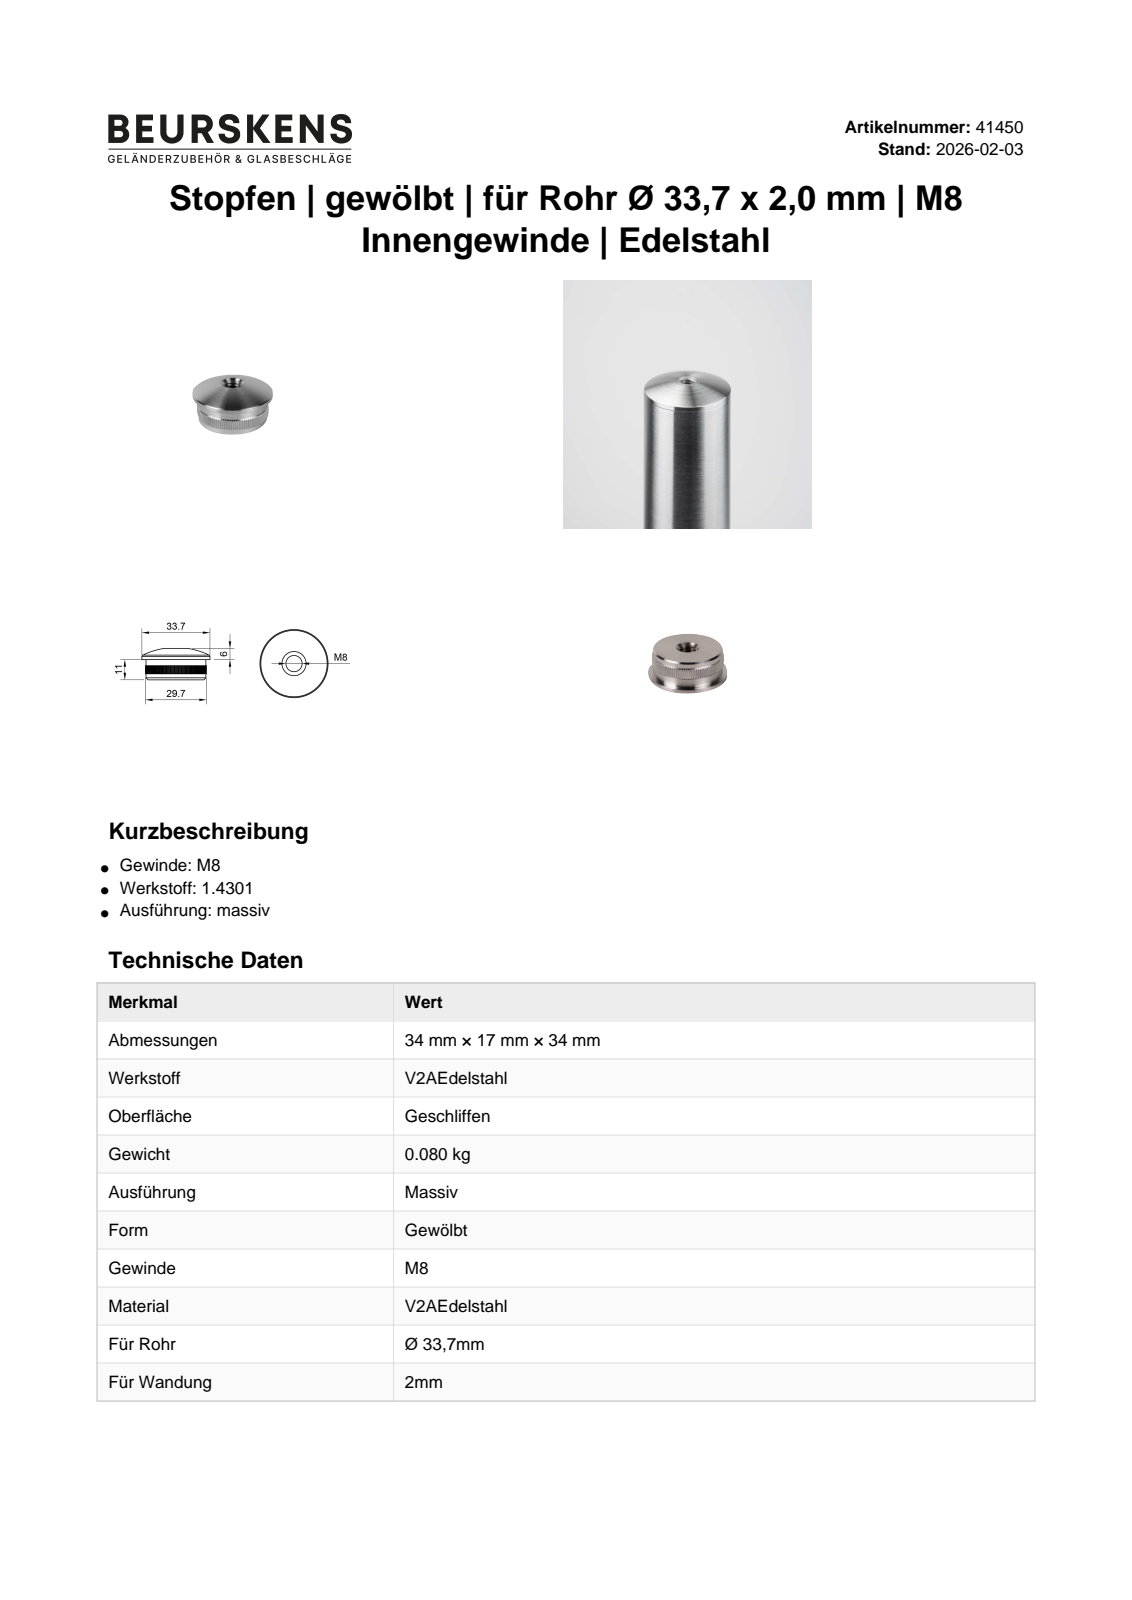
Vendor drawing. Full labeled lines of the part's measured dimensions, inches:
Part name (STEP PRODUCT): 41450
STEP written by: Autodesk Inventor 2022 (AUTOMOTIVE_DESIGN)
Units: inches
Bodies: 1 solid, 293 faces (4 planar, 284 cylindrical, 5 other)
Overall size (bounding box): 1.327 × 1.327 × 0.611
Volume: 0.586 in³ · Surface area: 5.086 in²
Round holes (diameter × count): ⌀0.315 ×1
Round bosses / shafts (diameter × count): ⌀1.327 ×1, ⌀1.165 ×1
Partial cylindrical surfaces — rounded edges, fillets, slot ends (radius × count): R0.005 ×140, R0.594 ×1
Main face-to-face distances: 0.394, 0.118, 0.276, 0.157
